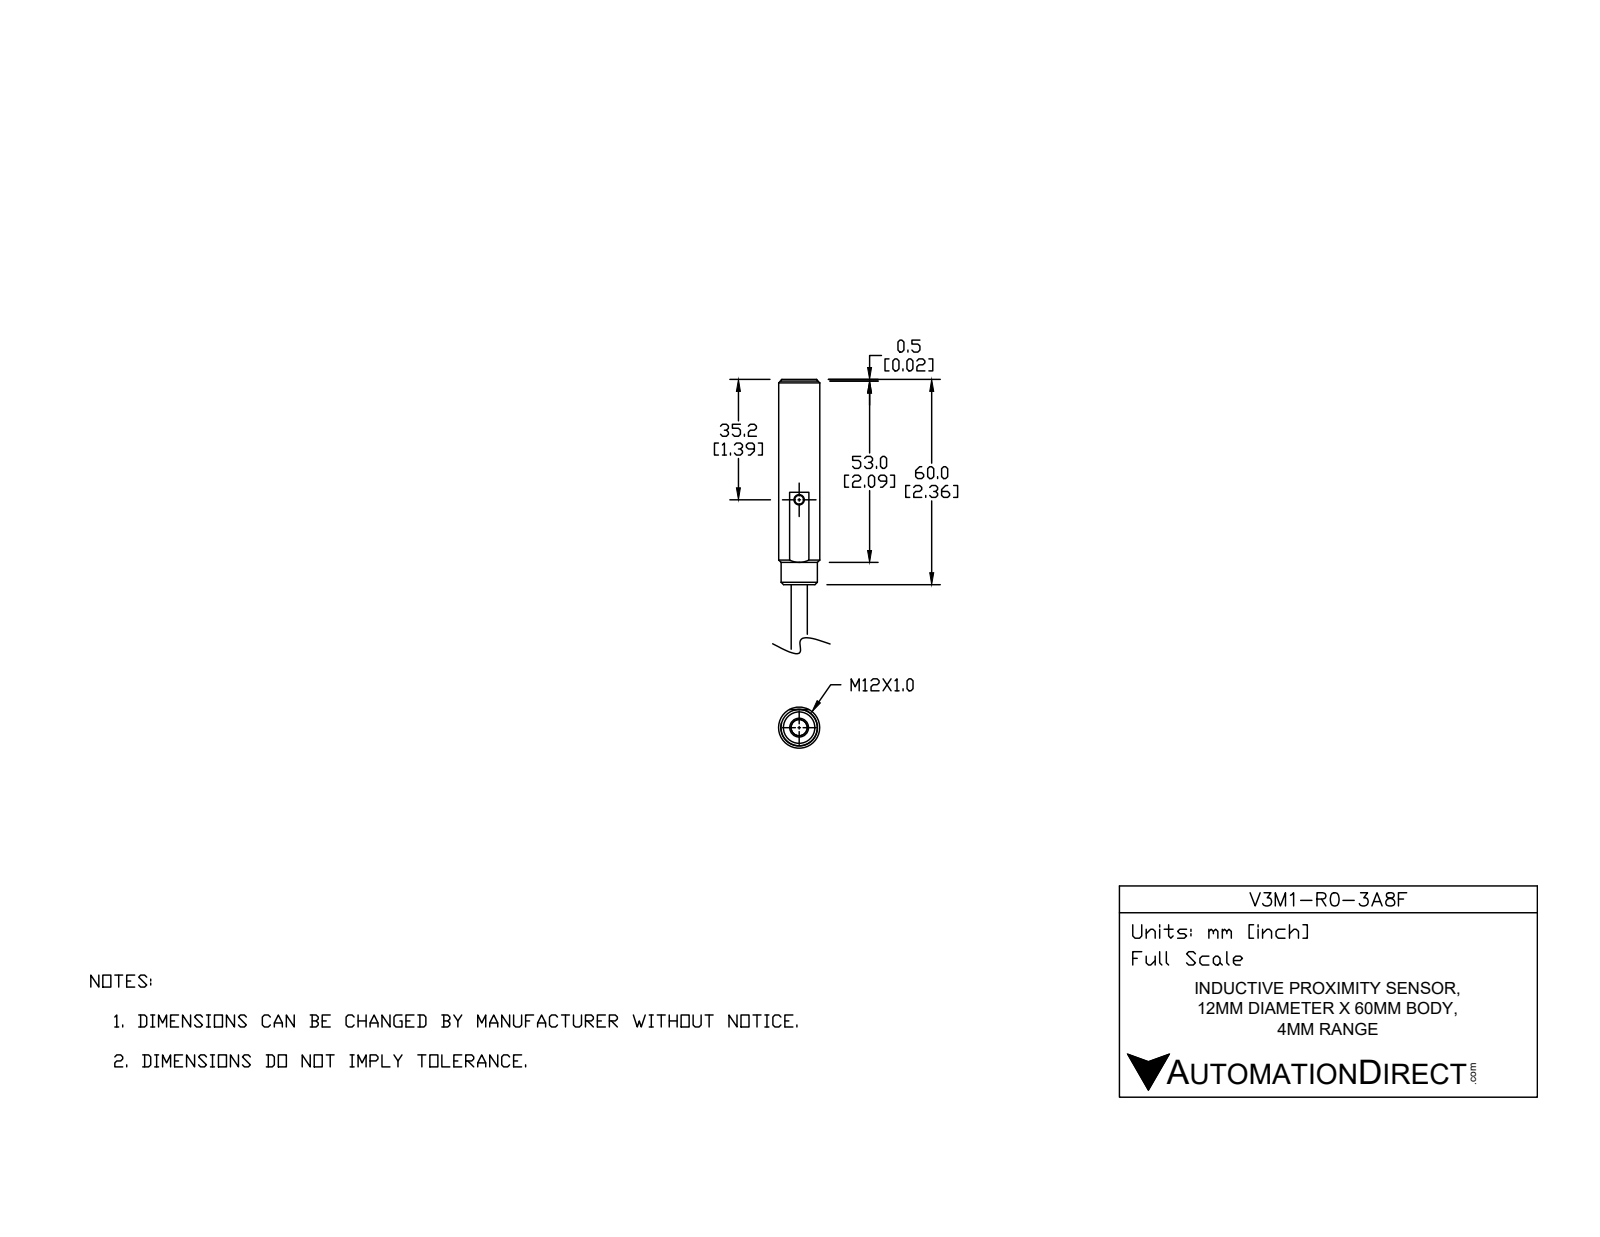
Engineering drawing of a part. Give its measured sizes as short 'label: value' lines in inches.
name: V3M1_3A_fig
written by: ST-DEVELOPER v16.7 (AUTOMOTIVE_DESIGN)
unit: in
bodies: 1 solid, 19 faces (8 planar, 5 cylindrical, 6 other)
size: 3.72 × 0.472 × 0.472
volume: 0.435 in³; area: 4.58 in²
holes: 1× ⌀0.102
bosses: 1× ⌀0.472, 1× ⌀0.417, 1× ⌀0.413, 1× ⌀0.185
face distances: 2.362, 3.72, 1.358, 0.02, 2.343, 3.701, 0.051, 1.299, 1.28, 1.063
